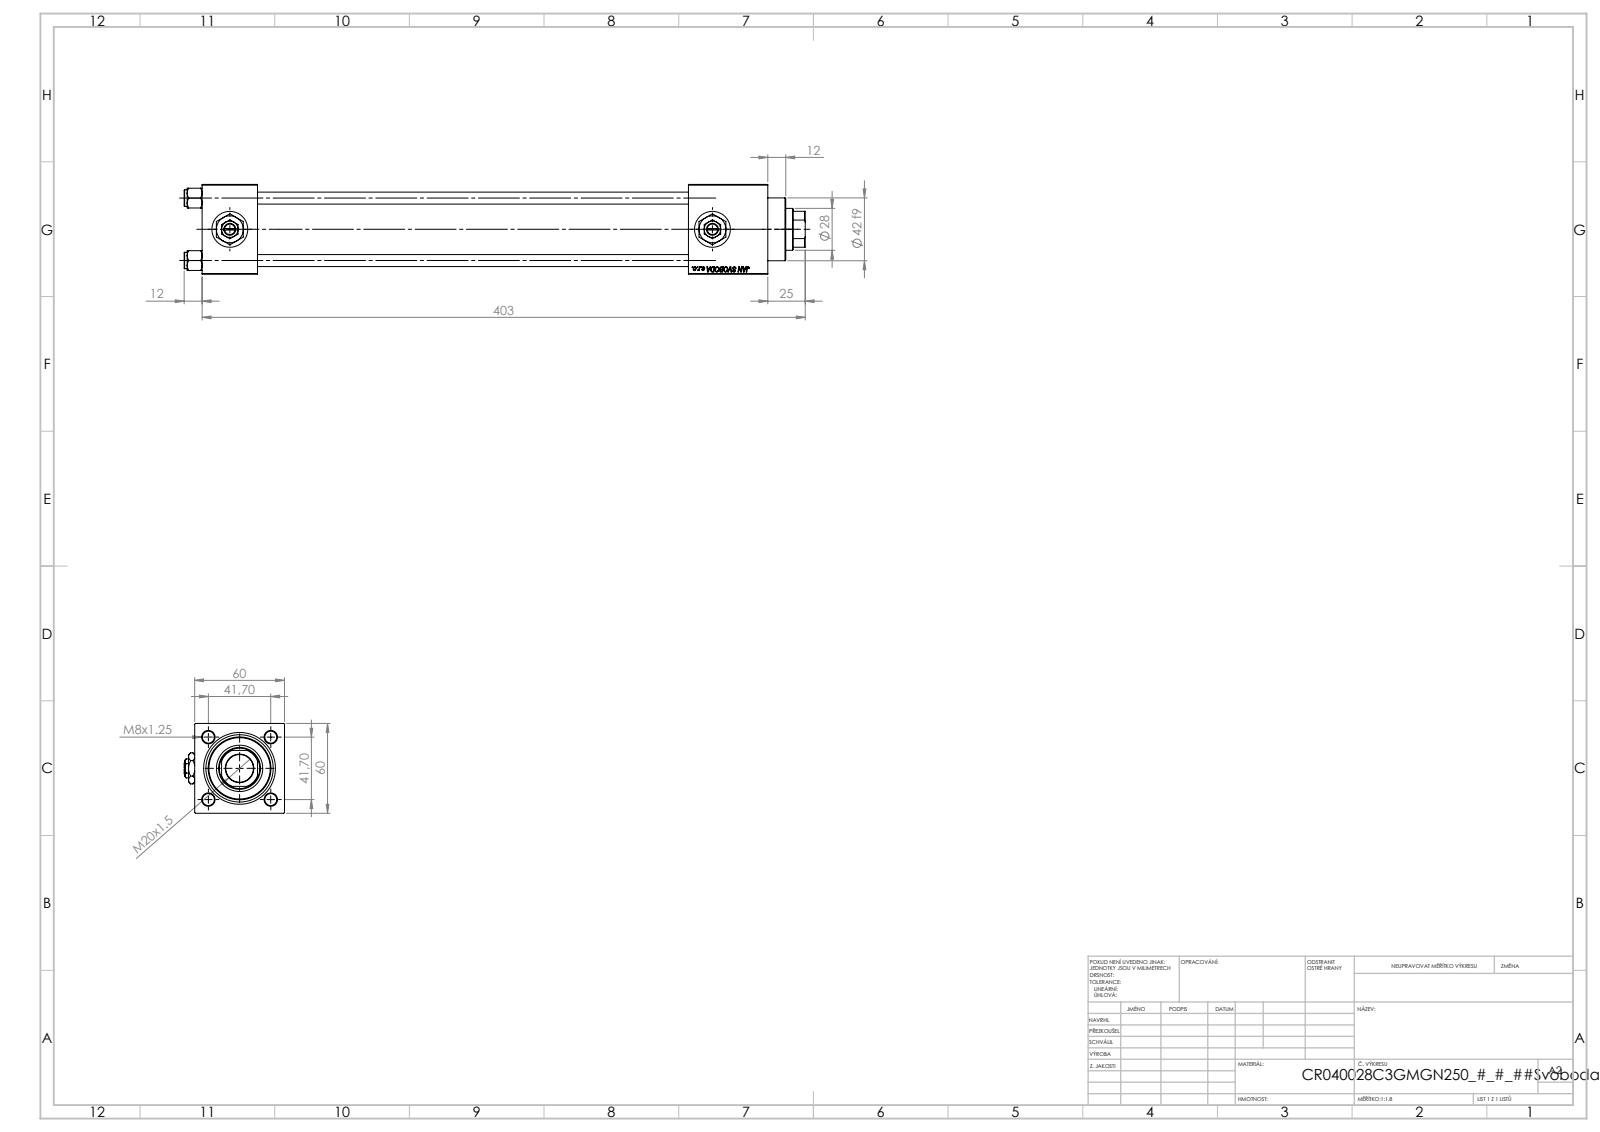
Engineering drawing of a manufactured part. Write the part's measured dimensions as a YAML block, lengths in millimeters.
part_name: "V215_VC_A; Zatka_pro_OIL_PORT; V215CR_VCP_C; NUT_M5_C (+2 more)"
step_written_by: "SolidWorks 2019 (CONFIG_CONTROL_DESIGN)"
units: millimeters
bodies: {solids: 13, faces: 1250, planar: 574, cylindrical: 98, other: 578}
overall_size: [415, 67, 60]
volume: 702016
surface_area: 219845
round_holes:
  - {diameter: 8, count: 4}
  - {diameter: 7, count: 2}
  - {diameter: 16.66, count: 2}
  - {diameter: 24, count: 2}
  - {diameter: 18.5, count: 1}
  - {diameter: 28, count: 1}
  - {diameter: 31, count: 1}
  - {diameter: 40, count: 1}
  - {diameter: 45, count: 1}
round_bosses_or_shafts:
  - {diameter: 11, count: 4}
  - {diameter: 46, count: 1}
  - {diameter: 42, count: 1}
partial_cylinders:
  - {radius: 13.5, count: 1}
face_to_face_distances: [60, 37, 325, 288, 53, 349.3, 312.3, 24.3, 378, 341]
hole_center_spacings: [29.49, 41.7, 58.97, 322.5]
